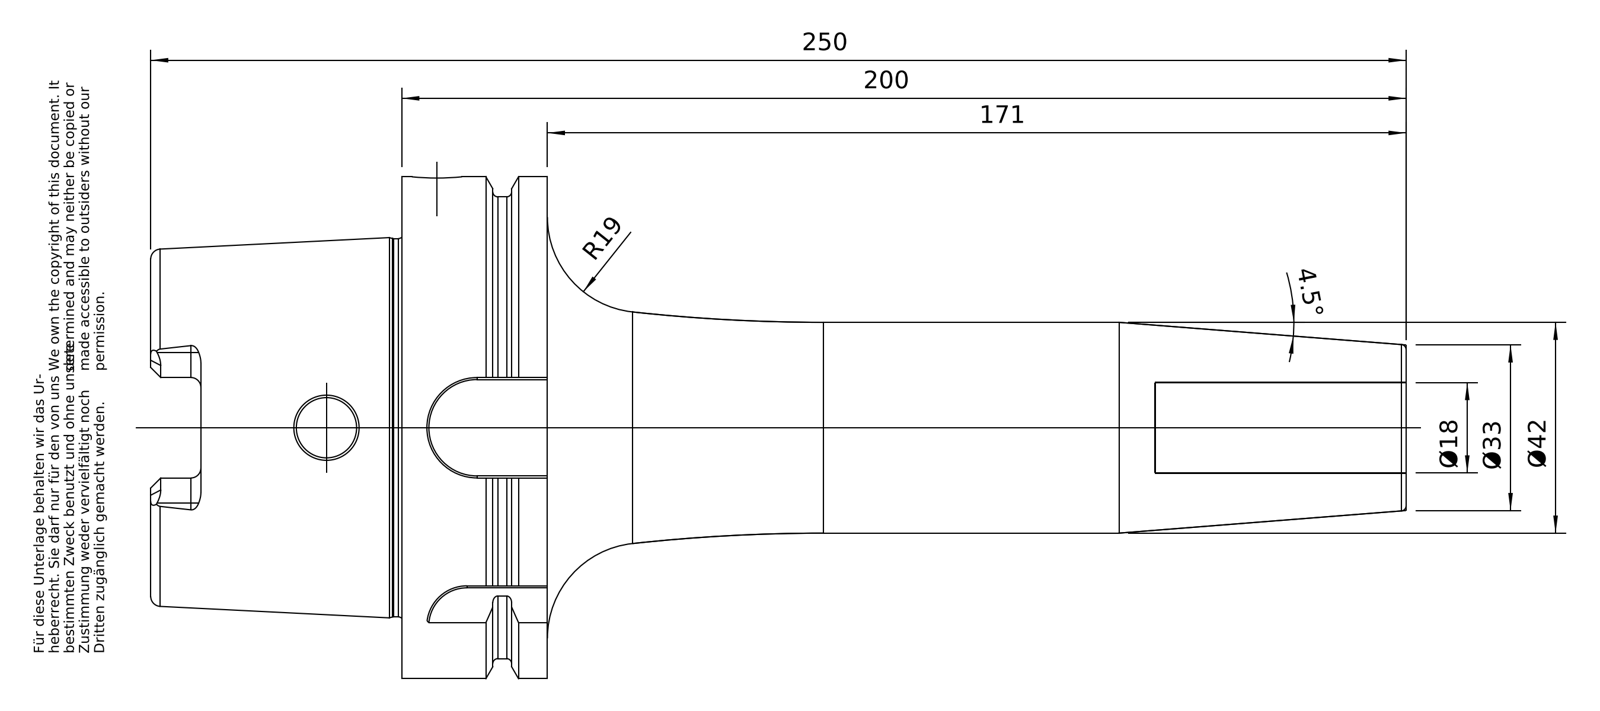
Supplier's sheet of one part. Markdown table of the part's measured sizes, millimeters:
| quantity | value |
| --- | --- |
| part name | A100-146-18 |
| STEP written by | PRO/ENGINEER BY PARAMETRIC TECHNOLOGY CORPORATION, 2010430 (CONFIG_CONTROL_DESIGN) |
| units | millimeters |
| bodies | 1 solid, 176 faces (50 planar, 51 cylindrical, 75 other) |
| overall size | 250 × 100 × 100 |
| volume | 484 016 mm³ |
| surface area | 73 368 mm² |
| round holes (diameter × count) | 10 × 1, 12 × 1, 18 × 1, 22.5 × 1, 24 × 1, 24.32 × 1, 24.5 × 1, 53 × 1, 63 × 1 |
| round bosses / shafts (diameter × count) | 100 × 1, 92 × 1, 75.36 × 1, 42 × 1 |
| partial cylindrical surfaces (radius × count) | 2 × 6, 5 × 4, 8 × 1, 10 × 1, 11 × 1 |
| main face-to-face distances | 29, 12.5, 16.5, 50, 62.5, 79, 200, 250, 187.5, 171 |
